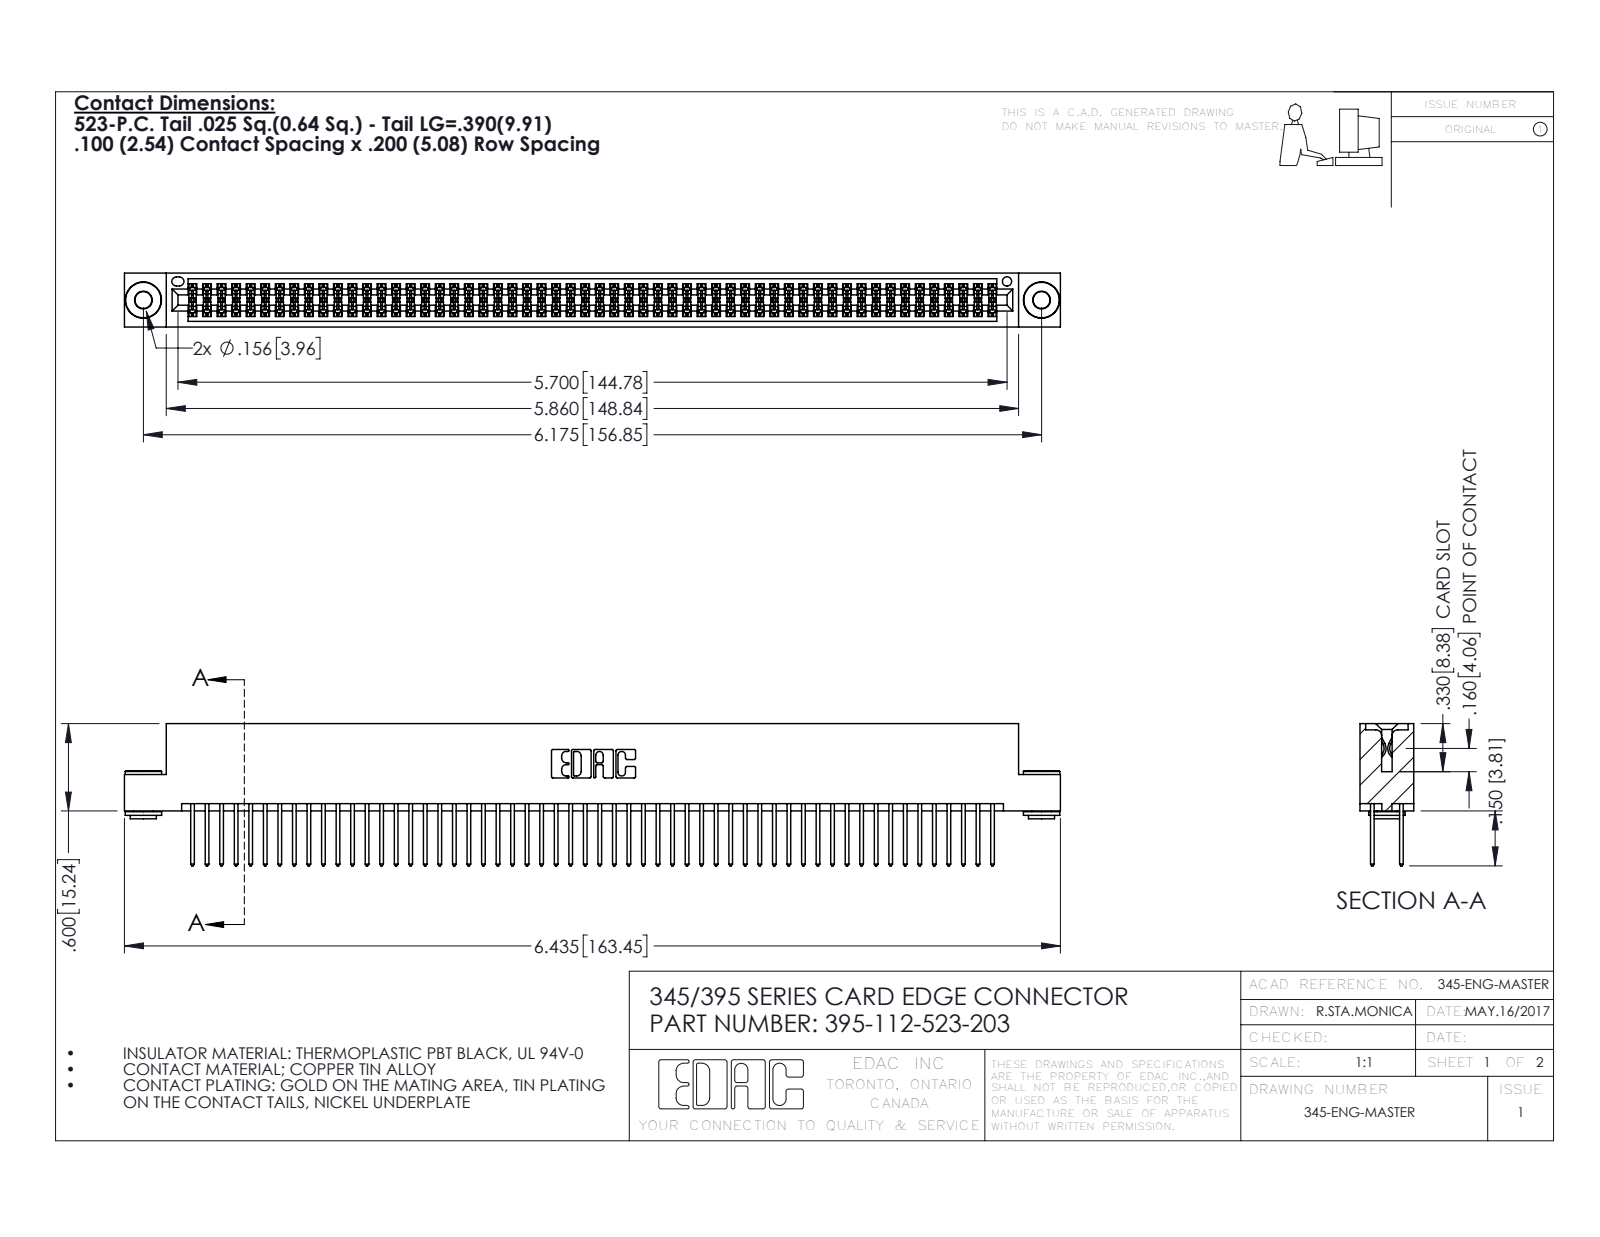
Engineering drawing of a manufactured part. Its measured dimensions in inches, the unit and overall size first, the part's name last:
Units: inches
Overall size (bounding box): 6.435 × 0.977 × 0.37
Round holes (diameter × count): ⌀0.116 ×2, ⌀0.156 ×2, ⌀0.064 ×1
Round bosses / shafts (diameter × count): ⌀0.25 ×2, ⌀0.18 ×2, ⌀0.136 ×2
Partial cylindrical surfaces — rounded edges, fillets, slot ends (radius × count): R0.006 ×168, R0.01 ×112, R0.01 ×22, R0.007 ×6, R0.031 ×6, R0.026 ×3, R0.014 ×2, R0.019 ×2
Main face-to-face distances: 0.072, 0.298, 0.2, 0.025, 0.098, 0.272, 0.37, 0.225, 0.175, 0.149
Hole centre spacings: 0.27, 5.939, 6.175
Volume: 0.992 in³ · Surface area: 39.58 in²
Bodies: 115 solids, 5764 faces (3786 planar, 1970 cylindrical, 8 other)
Part name (STEP PRODUCT): 345 Part_Flush Mounting Lugs - 0.156 Dia-TH; 395-112-523-203; 345-250-002_345-250-002-102; 345-292-001_345-293-123
STEP written by: SolidWorks 2016 (CONFIG_CONTROL_DESIGN)
